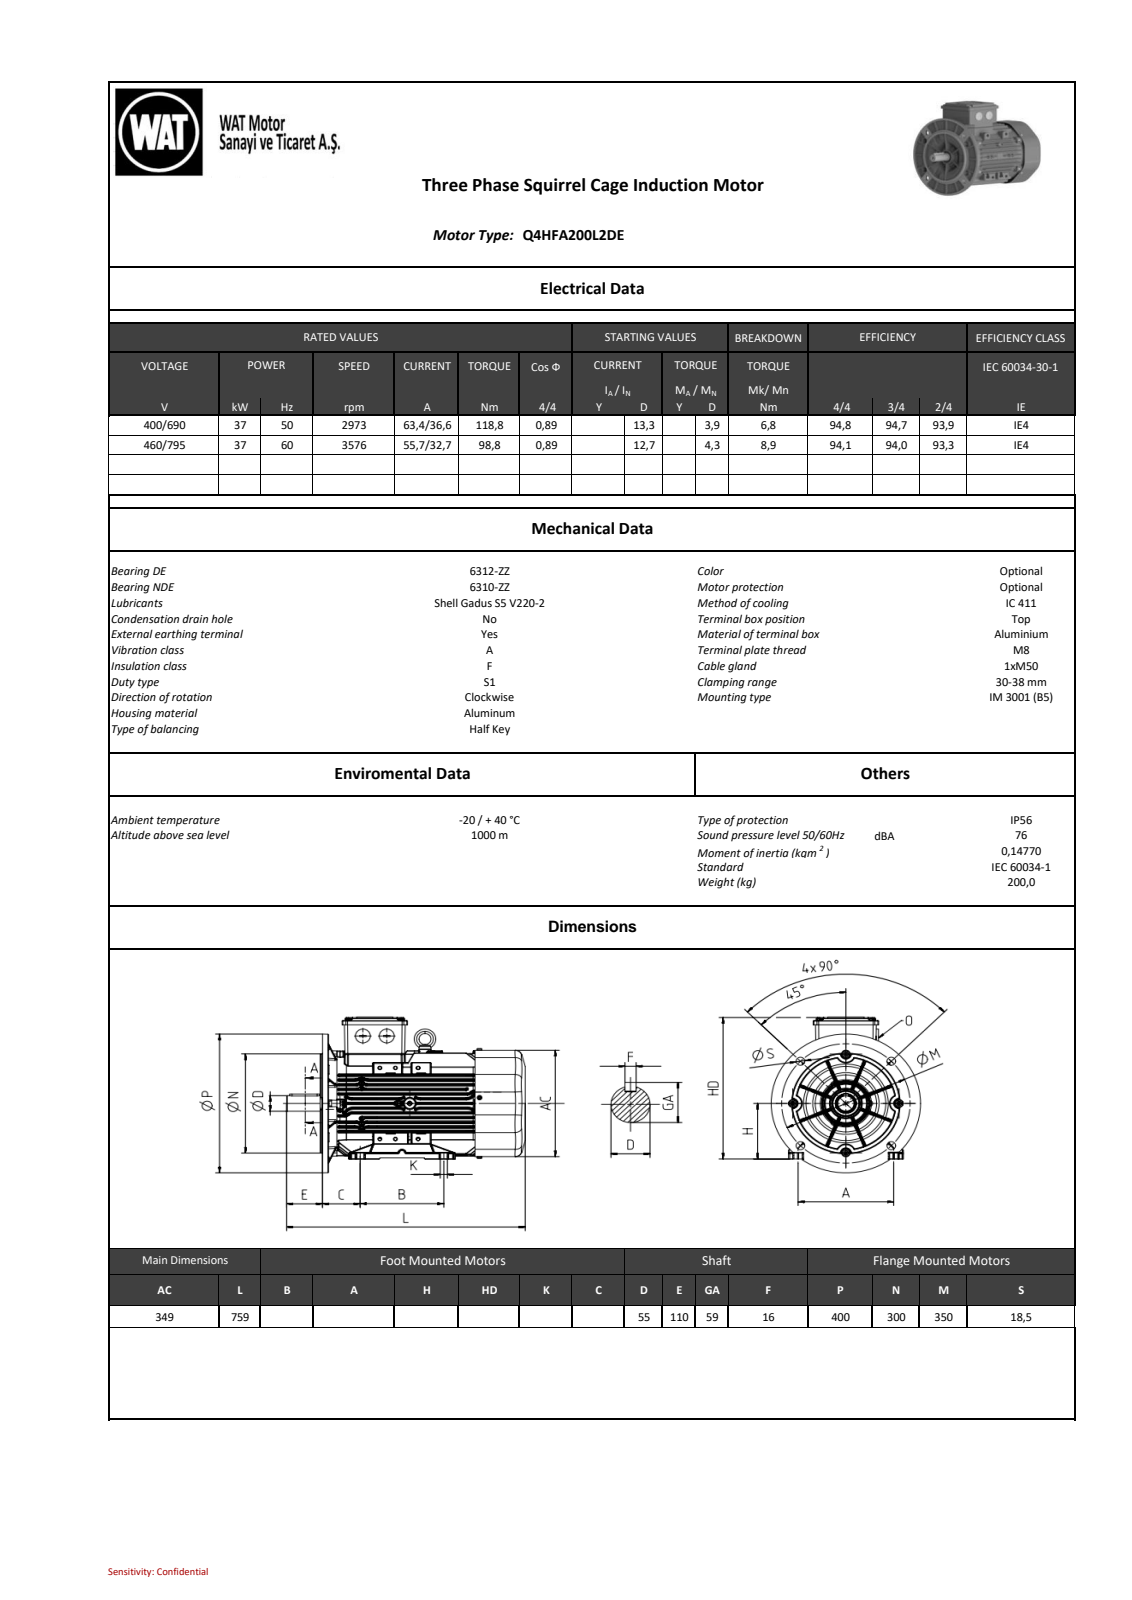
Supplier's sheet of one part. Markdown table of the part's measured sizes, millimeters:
| quantity | value |
| --- | --- |
| part name | model1_objects |
| STEP written by | SIEMENS PLM Software NX2206.8101 (AUTOMOTIVE_DESIGN) |
| units | millimeters |
| bodies | 0 solids, 13316 faces (3510 planar, 5362 cylindrical, 4444 other) |
| overall size | 759 × 454.84 × 399.69 |
| round holes (diameter × count) | 5.6 × 8, 6.8 × 8, 0.4 × 4, 4.3 × 4, 6.5 × 4, 9 × 4, 18.5 × 4, 44 × 4, 4 × 3, 5.5 × 3, 3.2 × 2, 9.44 × 2 |
| round bosses / shafts (diameter × count) | 56 × 4, 50 × 4, 12 × 4, 10 × 4, 9.5 × 4, 6 × 4, 5.49 × 4, 5 × 4 |
| partial cylindrical surfaces (radius × count) | 0.5 × 1658, 2 × 981, 1 × 868, 5 × 274, 3 × 151, 0.1 × 122, 4 × 64, 1 × 36 |
| main face-to-face distances | 1.2, 6, 16.21, 3, 32.48, 16.27, 573, 15, 171.05, 173.83 |
| hole center spacings | 129.23, 310.46, 136, 78.16, 169.96, 322, 156, 161 |
